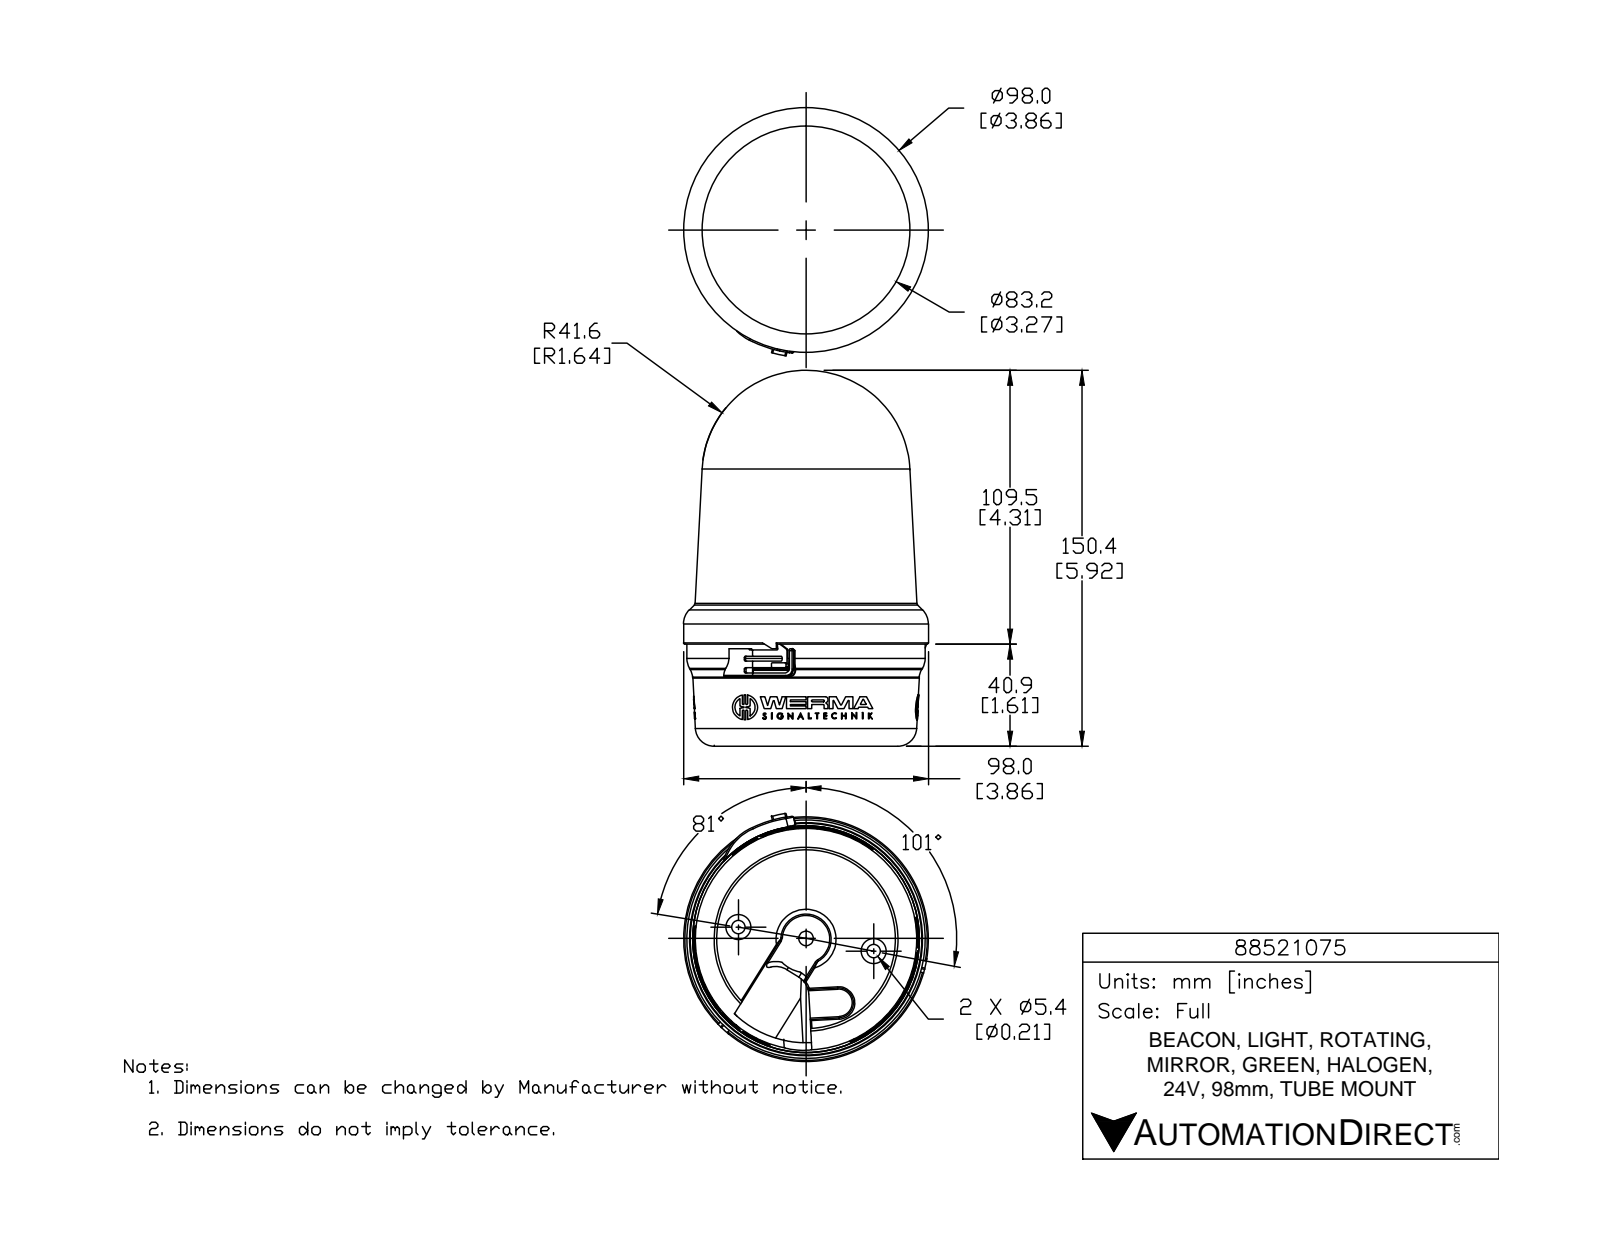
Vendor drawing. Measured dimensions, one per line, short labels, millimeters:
name: 88521075
written by: SolidWorks 2015 (AUTOMOTIVE_DESIGN)
unit: mm
bodies: 1 solid, 1006 faces (554 planar, 189 cylindrical, 263 other)
size: 201 × 99.4 × 98
volume: 896 400 mm³; area: 58 960 mm²
holes: 3× ⌀2, 1× ⌀25.7, 1× ⌀26
bosses: 3× ⌀11.5, 3× ⌀2.9, 1× ⌀98, 1× ⌀35.8, 1× ⌀32
rounds: 12× R0.5, 9× R0.2, 6× R0.2, 6× R0.4, 6× R0.4, 6× R0.4, 6× R6.7, 3× R0.2
face distances: 56.2, 11.7, 68, 8.5, 3.2, 64.7, 66.1, 62.9, 54.4, 1.9
